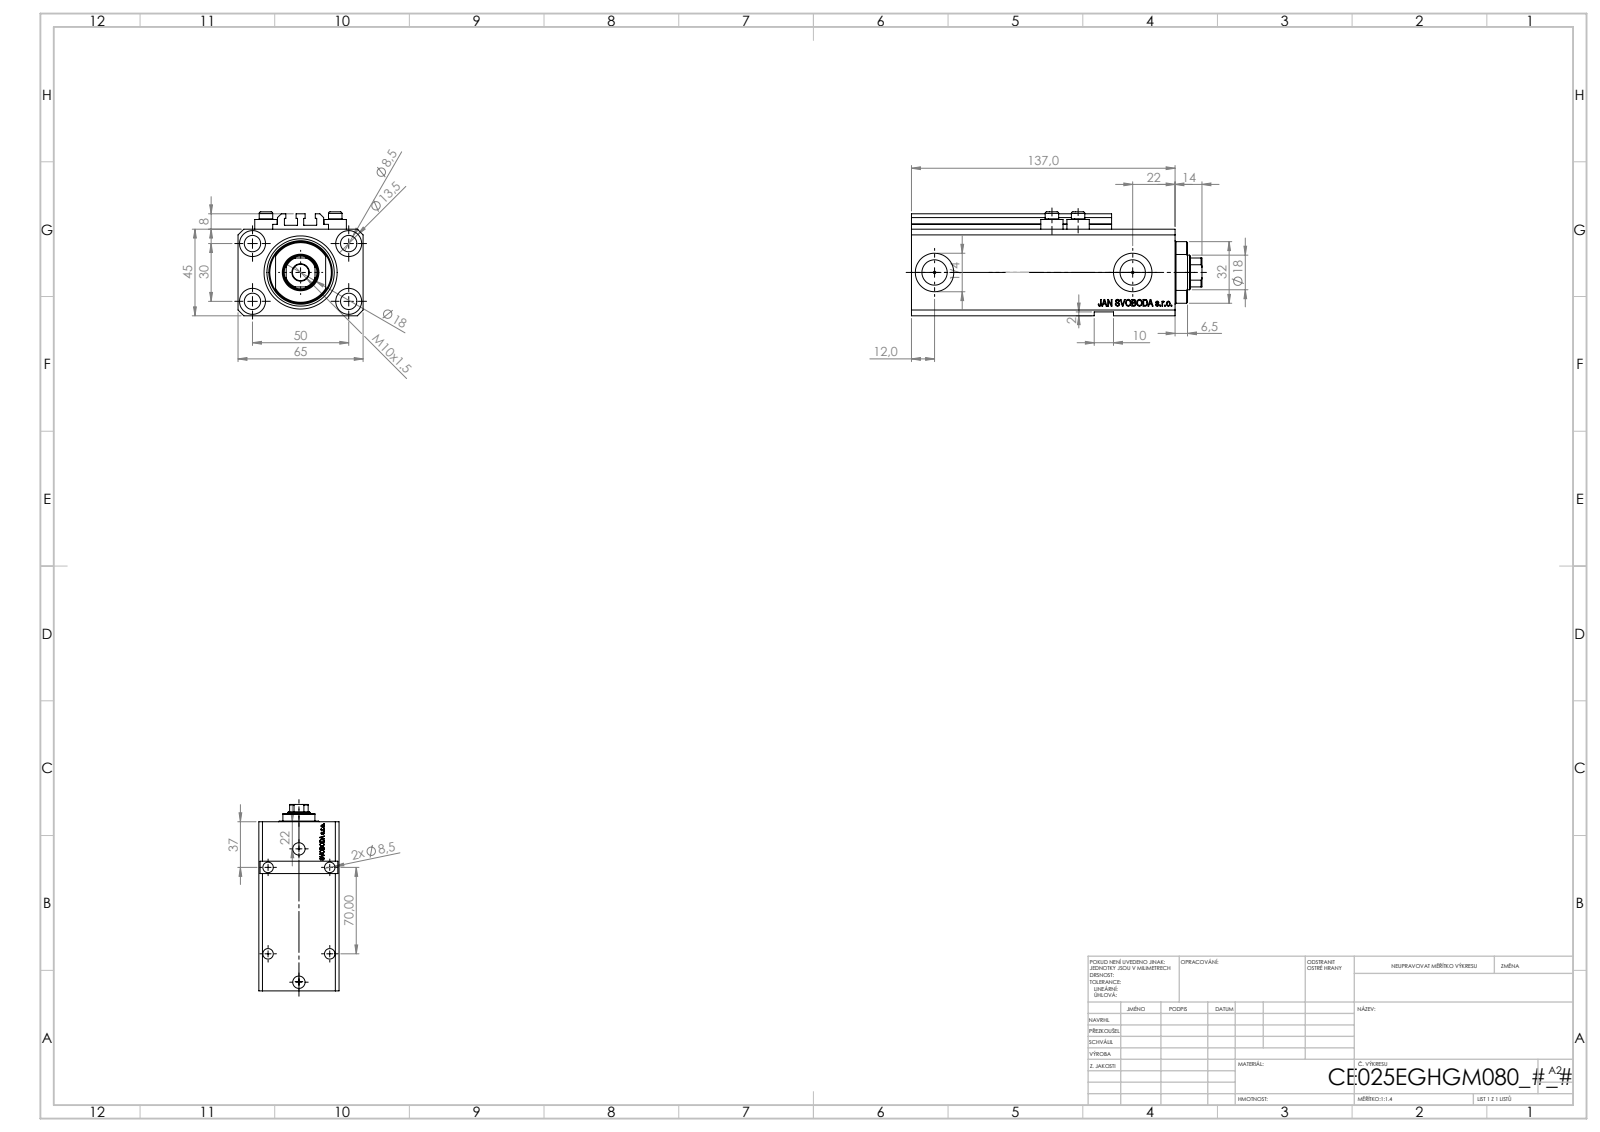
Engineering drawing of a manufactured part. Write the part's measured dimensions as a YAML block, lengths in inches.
part_name: "V250CE_C_VCP; ALLEN BOLT V250CE; V250CE_VC_E; V250CE_E_Body"
step_written_by: "SolidWorks 2019 (CONFIG_CONTROL_DESIGN)"
units: inches
bodies: {solids: 8, faces: 1087, planar: 511, cylindrical: 146, other: 430}
overall_size: [5.945, 2.559, 2.126]
volume: 21.39
surface_area: 145
round_holes:
  - {diameter: 0.335, count: 9}
  - {diameter: 0.049, count: 4}
  - {diameter: 0.157, count: 4}
  - {diameter: 0.531, count: 4}
  - {diameter: 0.394, count: 2}
  - {diameter: 0.518, count: 2}
  - {diameter: 0.787, count: 2}
  - {diameter: 0.709, count: 1}
  - {diameter: 0.984, count: 1}
  - {diameter: 1.496, count: 1}
round_bosses_or_shafts:
  - {diameter: 0.457, count: 4}
  - {diameter: 0.276, count: 4}
partial_cylinders:
  - {radius: 0.008, count: 10}
  - {radius: 0.335, count: 1}
  - {radius: 0.63, count: 1}
face_to_face_distances: [1.772, 2.559, 1.85, 0.079, 4.843, 0.098, 0.551, 0.394, 5.394, 0.807]
hole_center_spacings: [1.148, 1.969, 0.535, 0.595, 1.098, 1.181, 1.323, 1.324]
